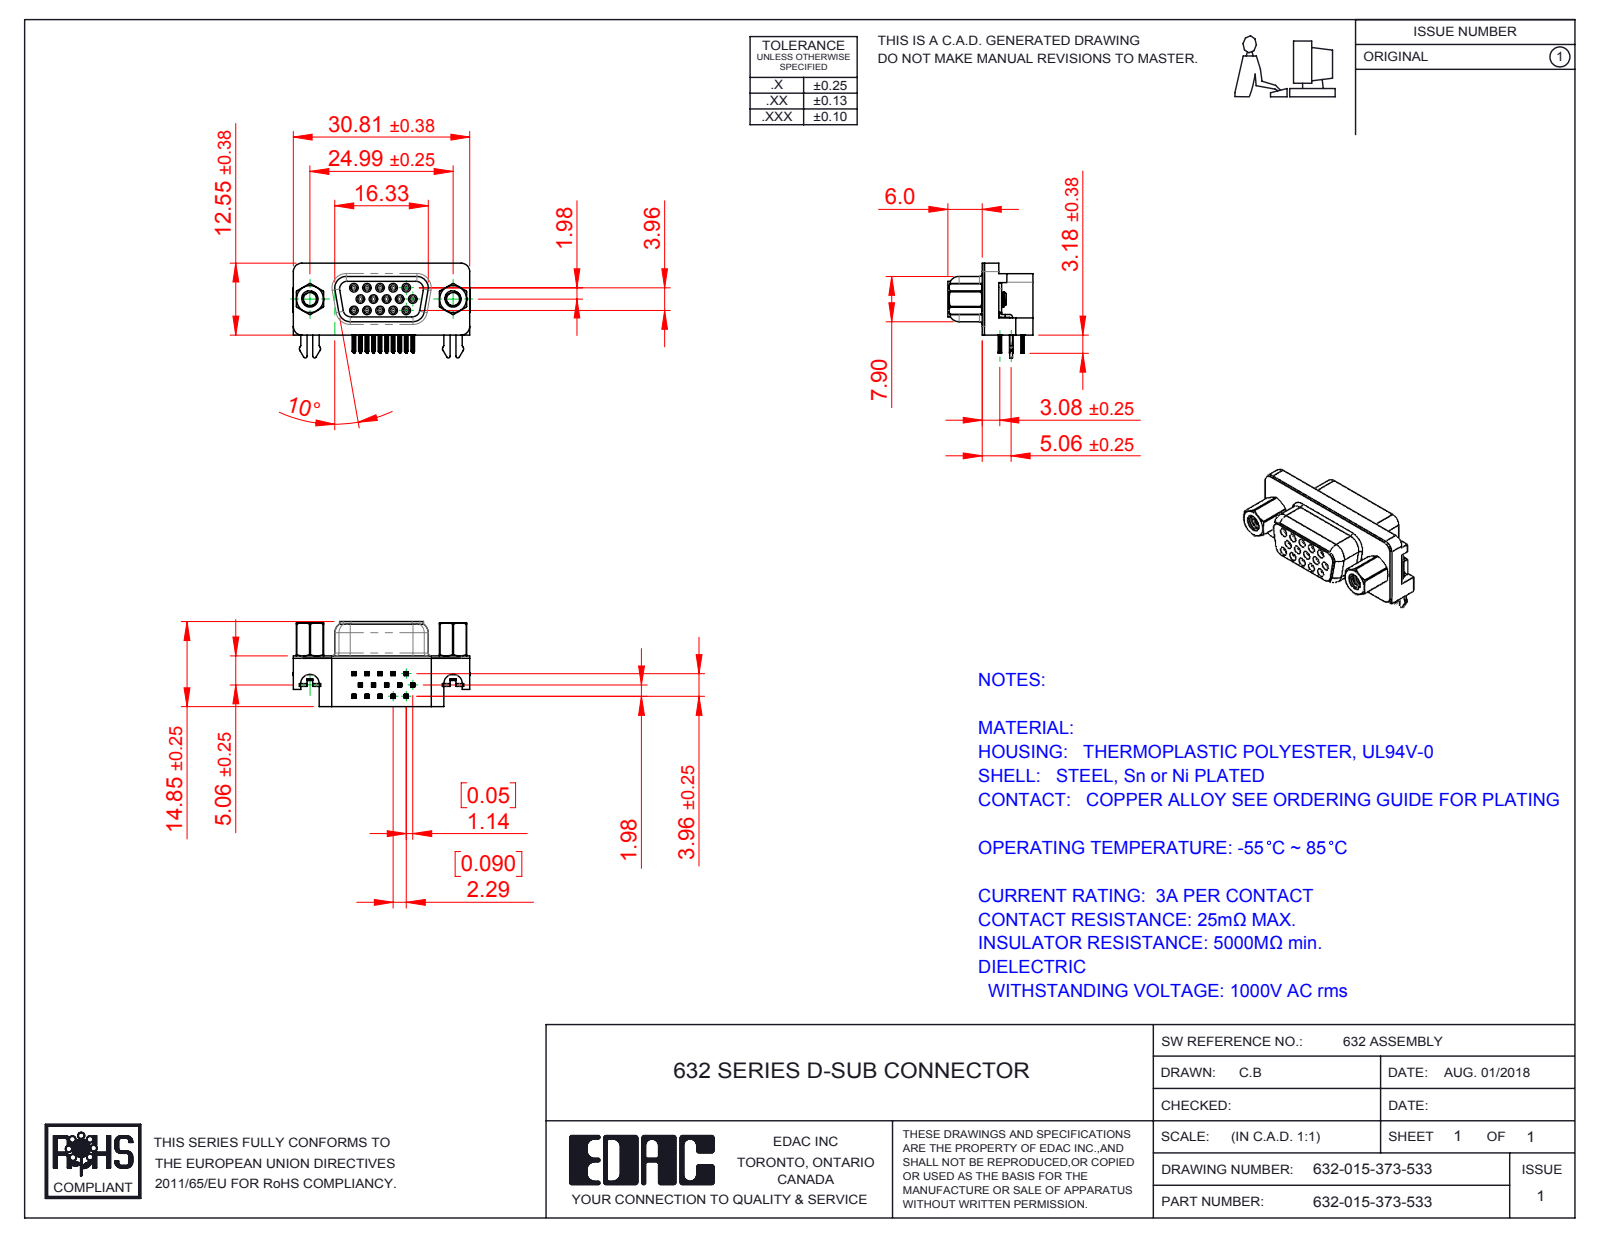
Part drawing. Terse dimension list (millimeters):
name: 632 Shell_9 Socket; 632 Contact Middle; 632 Contact Top; 632-015-373-533 (+5 more)
written by: SolidWorks 2016 (CONFIG_CONTROL_DESIGN)
unit: mm
bodies: 21 solids, 2376 faces (996 planar, 646 cylindrical, 734 other)
size: 30.89 × 16.55 × 14.85
volume: 3 051 mm³; area: 5 177 mm²
holes: 15× ⌀0.8, 15× ⌀0.9, 2× ⌀2.29, 2× ⌀4, 2× ⌀4.8, 2× ⌀5
bosses: 15× ⌀1.2, 2× ⌀4.9, 2× ⌀2.79
rounds: 120× R0.1, 60× R0.15, 30× R0.35, 15× R0.34, 11× R1, 10× R0.28, 10× R0.5, 8× R1.35
face distances: 0.4, 1.98, 8.45, 8.85, 2.9, 2.5, 5.95, 6.7, 7.05, 3.17
hole spacings: 2.28, 2.29, 3.96, 4.57, 6.05, 3.97, 4.58, 6.86
